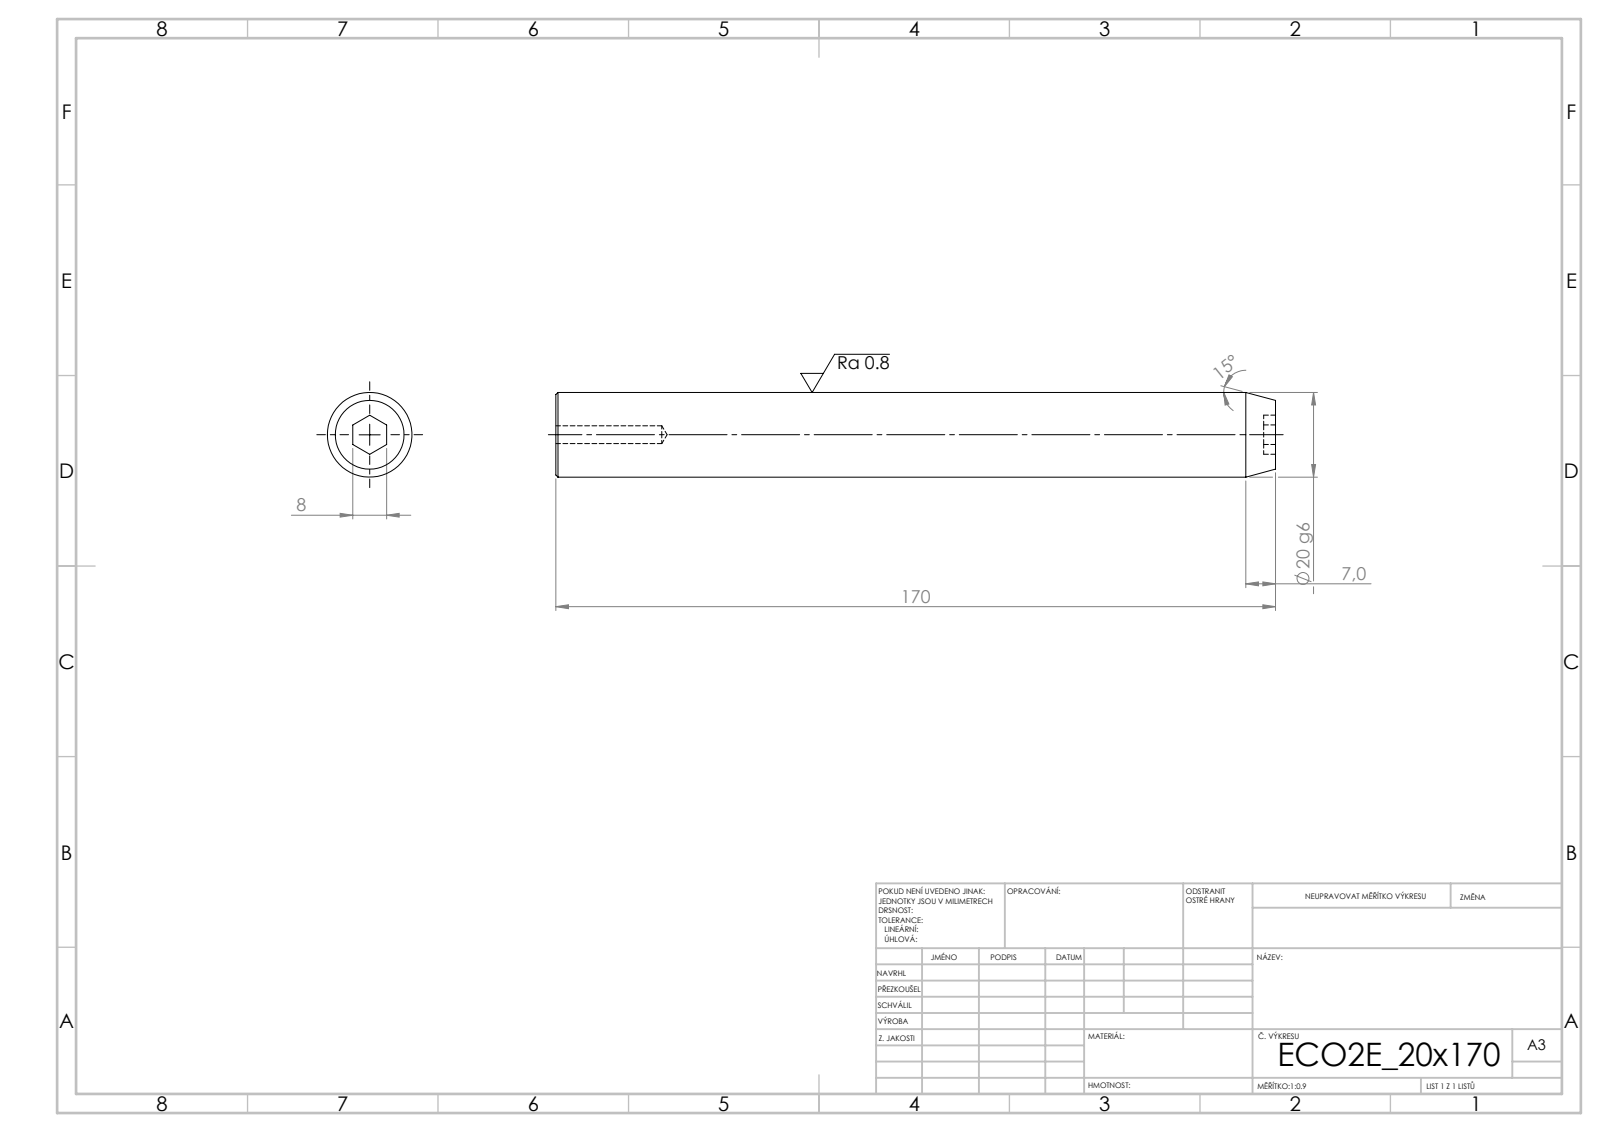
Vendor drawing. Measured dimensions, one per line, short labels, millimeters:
written by: SolidWorks 2019 (CONFIG_CONTROL_DESIGN)
unit: mm
bodies: 1 solid, 19 faces (9 planar, 4 cylindrical, 6 other)
size: 170 × 20 × 20
volume: 52 505 mm³; area: 11 567 mm²
holes: 1× ⌀4.2
bosses: 1× ⌀20
face distances: 170, 2.8, 167.2, 8
